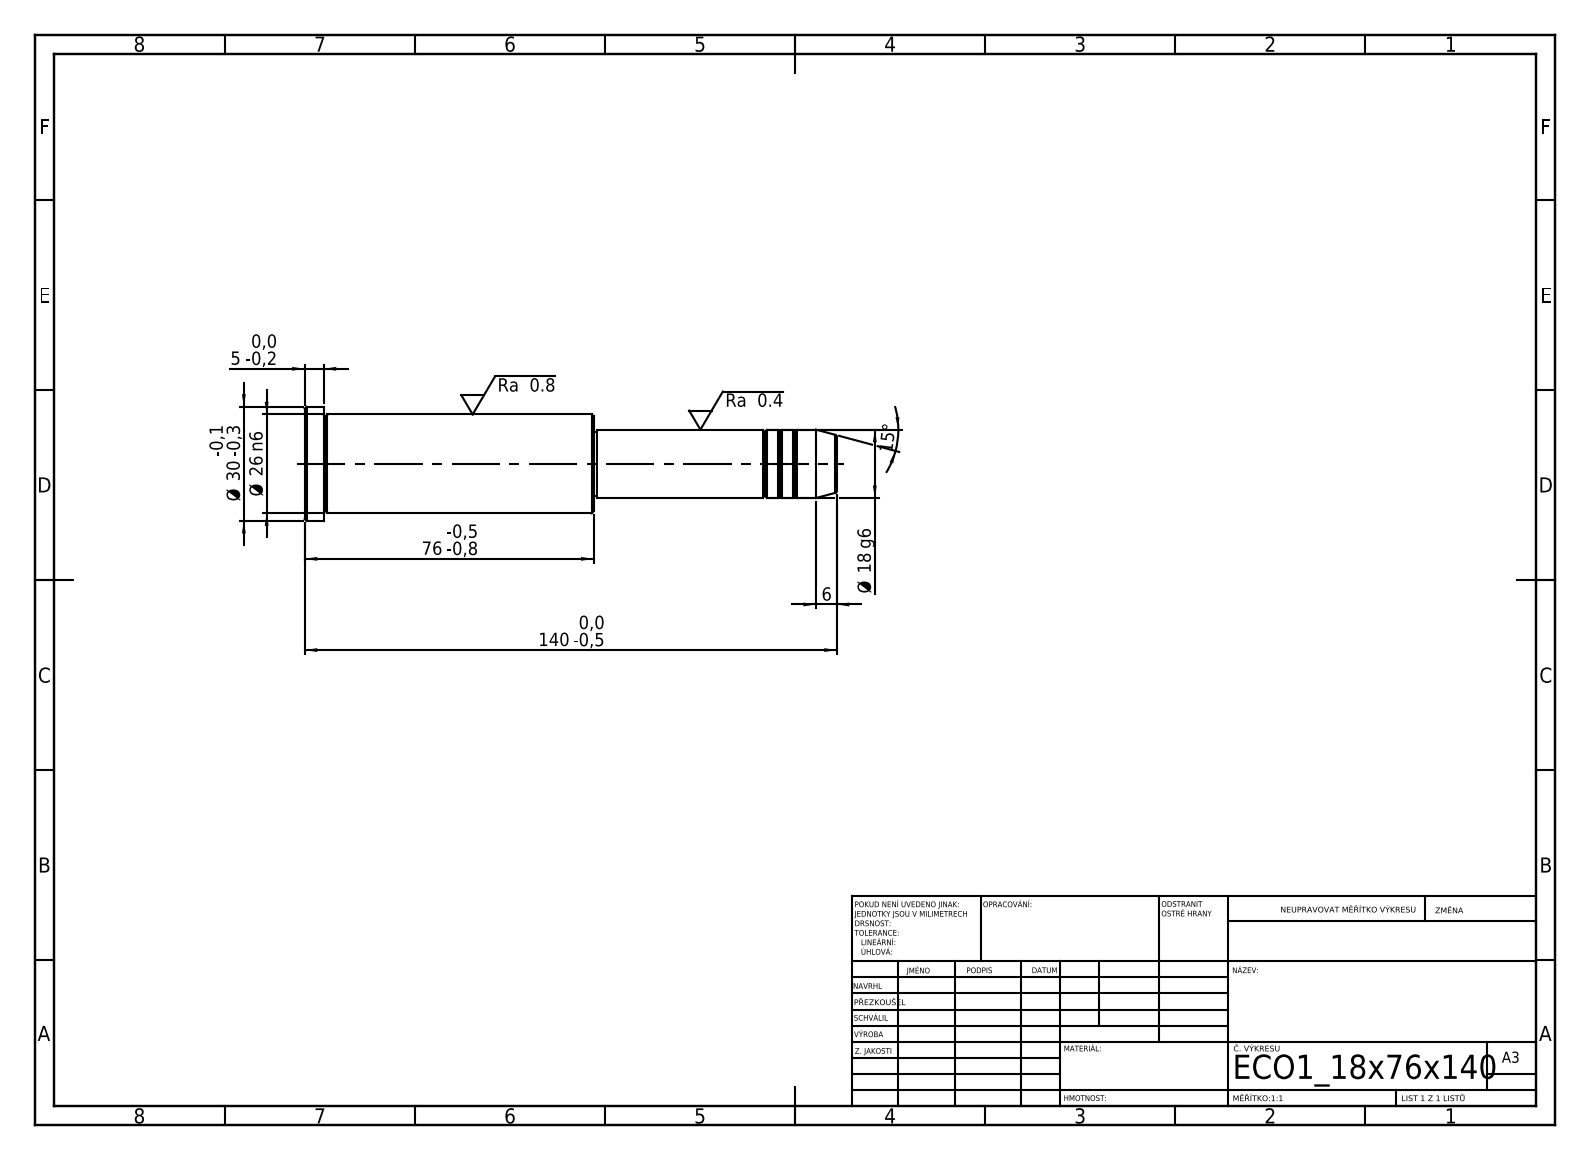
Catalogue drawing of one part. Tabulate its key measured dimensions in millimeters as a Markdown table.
| quantity | value |
| --- | --- |
| STEP written by | SolidWorks 2019 (CONFIG_CONTROL_DESIGN) |
| units | millimeters |
| bodies | 1 solid, 43 faces (5 planar, 14 cylindrical, 24 other) |
| overall size | 140 × 30 × 30 |
| volume | 57 152 mm³ |
| surface area | 11 337 mm² |
| round bosses / shafts (diameter × count) | 30 × 1, 26 × 1, 18 × 1, 17 × 1 |
| main face-to-face distances | 76, 71, 5, 64, 135, 140, 63, 1, 72, 77 |
